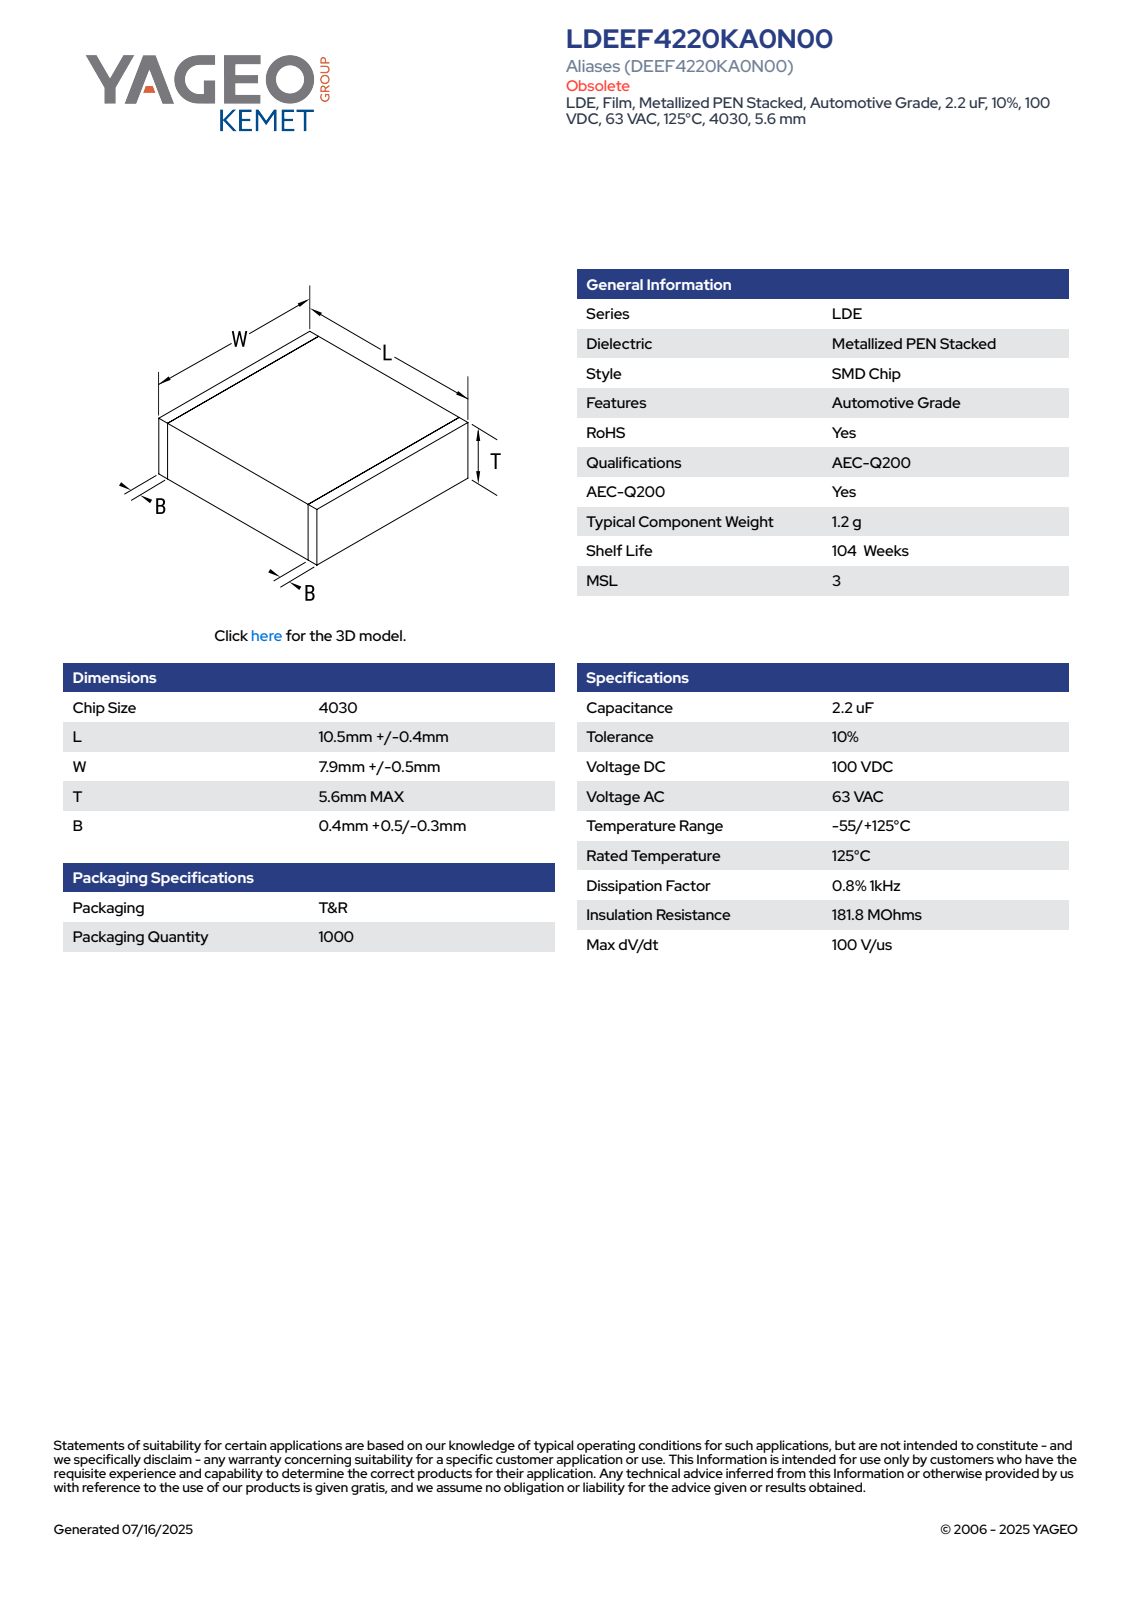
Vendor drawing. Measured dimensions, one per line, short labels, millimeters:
name: CFS_LDELDB_4030_L10.9W8.4T5.6B0.9
written by: SolidWorks 2020 (AUTOMOTIVE_DESIGN)
unit: mm
bodies: 4 solids, 73 faces (73 planar, 0 cylindrical, 0 other)
size: 10.9 × 8.4 × 5.6
volume: 510 mm³; area: 405 mm²
face distances: 5.58, 8.38, 10.9, 5.59, 8.39, 5.6, 8.4, 0.5, 10.4, 9.9
